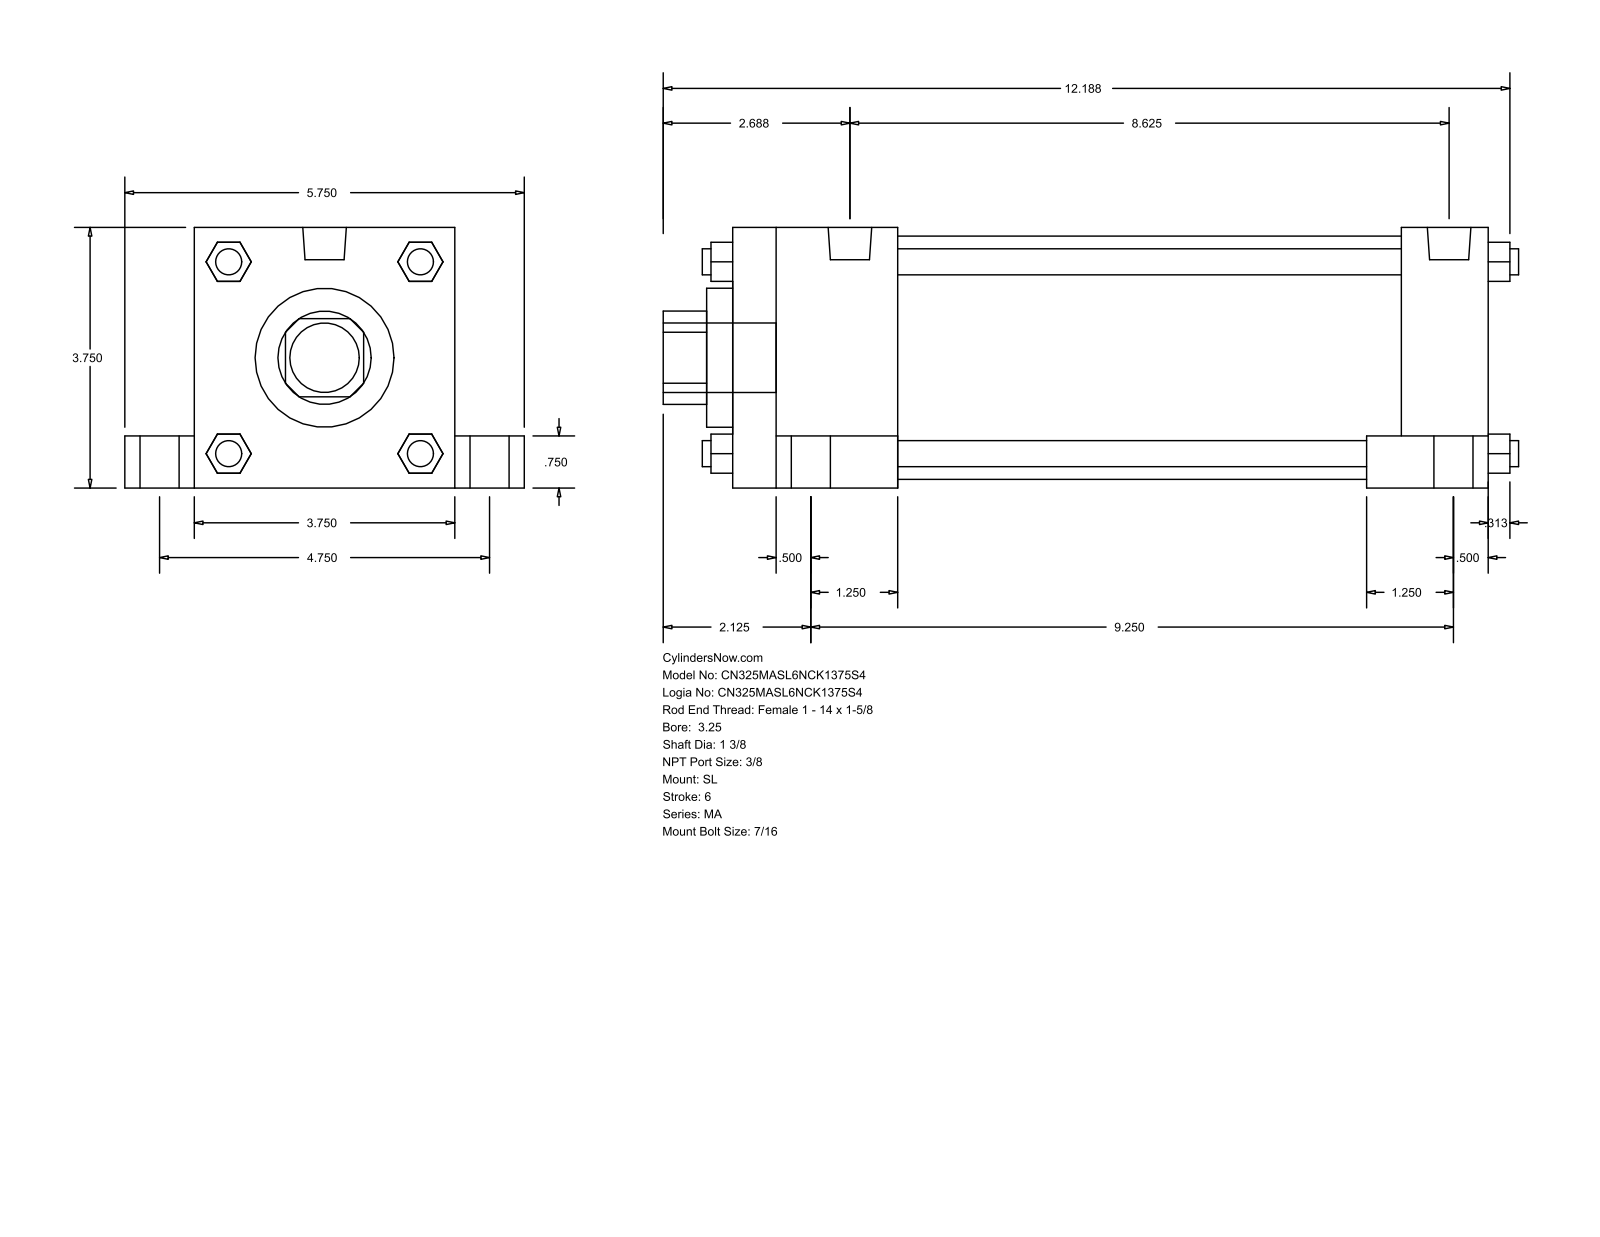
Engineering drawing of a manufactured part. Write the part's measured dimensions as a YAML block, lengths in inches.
part_name: "MA_SL__0325_1.375"
step_written_by: "GSSL Pune (CONFIG_CONTROL_DESIGN)"
units: inches
bodies: {solids: 0, faces: 148, planar: 112, cylindrical: 36, other: 0}
overall_size: [12.313, 5.75, 3.75]
round_holes:
  - {diameter: 1.375, count: 1}
  - {diameter: 2, count: 1}
  - {diameter: 3.5, count: 1}
round_bosses_or_shafts:
  - {diameter: 0.813, count: 4}
  - {diameter: 0.563, count: 4}
  - {diameter: 0.437, count: 4}
  - {diameter: 0.375, count: 4}
  - {diameter: 0.627, count: 2}
  - {diameter: 1, count: 1}
partial_cylinders:
  - {radius: 0.672, count: 1}
face_to_face_distances: [3.75, 10.875, 1, 4.75, 9.625, 1.25, 2.375, 7.25, 8.5, 0.75]
